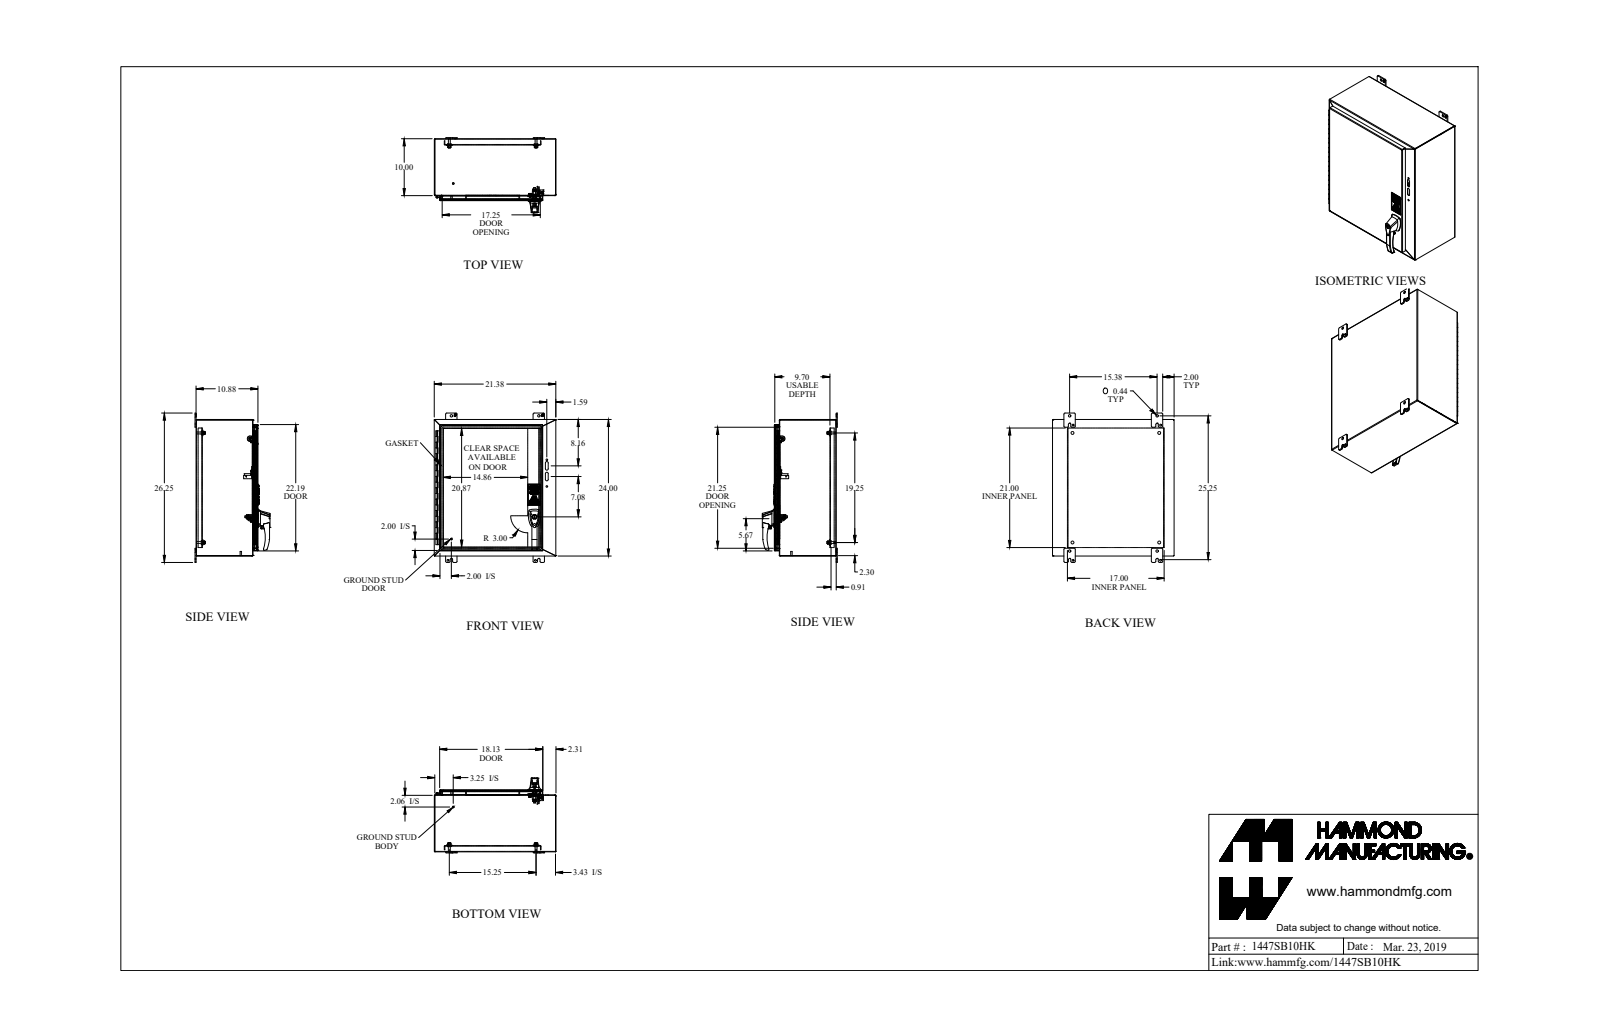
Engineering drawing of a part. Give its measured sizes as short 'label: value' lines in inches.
name: 1447SB10HK
written by: SolidWorks 2019 (AUTOMOTIVE_DESIGN)
unit: in
bodies: 49 solids, 1126 faces (709 planar, 318 cylindrical, 99 other)
size: 26.25 × 21.375 × 13.177
volume: 215.5 in³; area: 5 382 in²
holes: 5× ⌀0.313, 4× ⌀0.176, 4× ⌀0.437, 4× ⌀0.5, 2× ⌀0.156, 2× ⌀0.173, 2× ⌀0.215, 2× ⌀0.25, 2× ⌀0.265, 2× ⌀0.281, 2× ⌀0.307, 2× ⌀0.413
bosses: 8× ⌀0.375, 7× ⌀0.25, 4× ⌀1, 4× ⌀0.65, 4× ⌀0.33, 4× ⌀0.156, 2× ⌀0.5, 2× ⌀0.402
rounds: 28× R0.079, 24× R0.188, 12× R0.25, 11× R0.125, 8× R0.007, 8× R0.03, 8× R0.218, 7× R0.06
face distances: 0.072, 10.803, 21.303, 10.731, 23.928, 10.875, 0.095, 9.771, 9.699, 1.032
hole spacings: 15.25, 15.375, 1.111, 14.674, 24.559, 1.735, 1.736, 1.855
